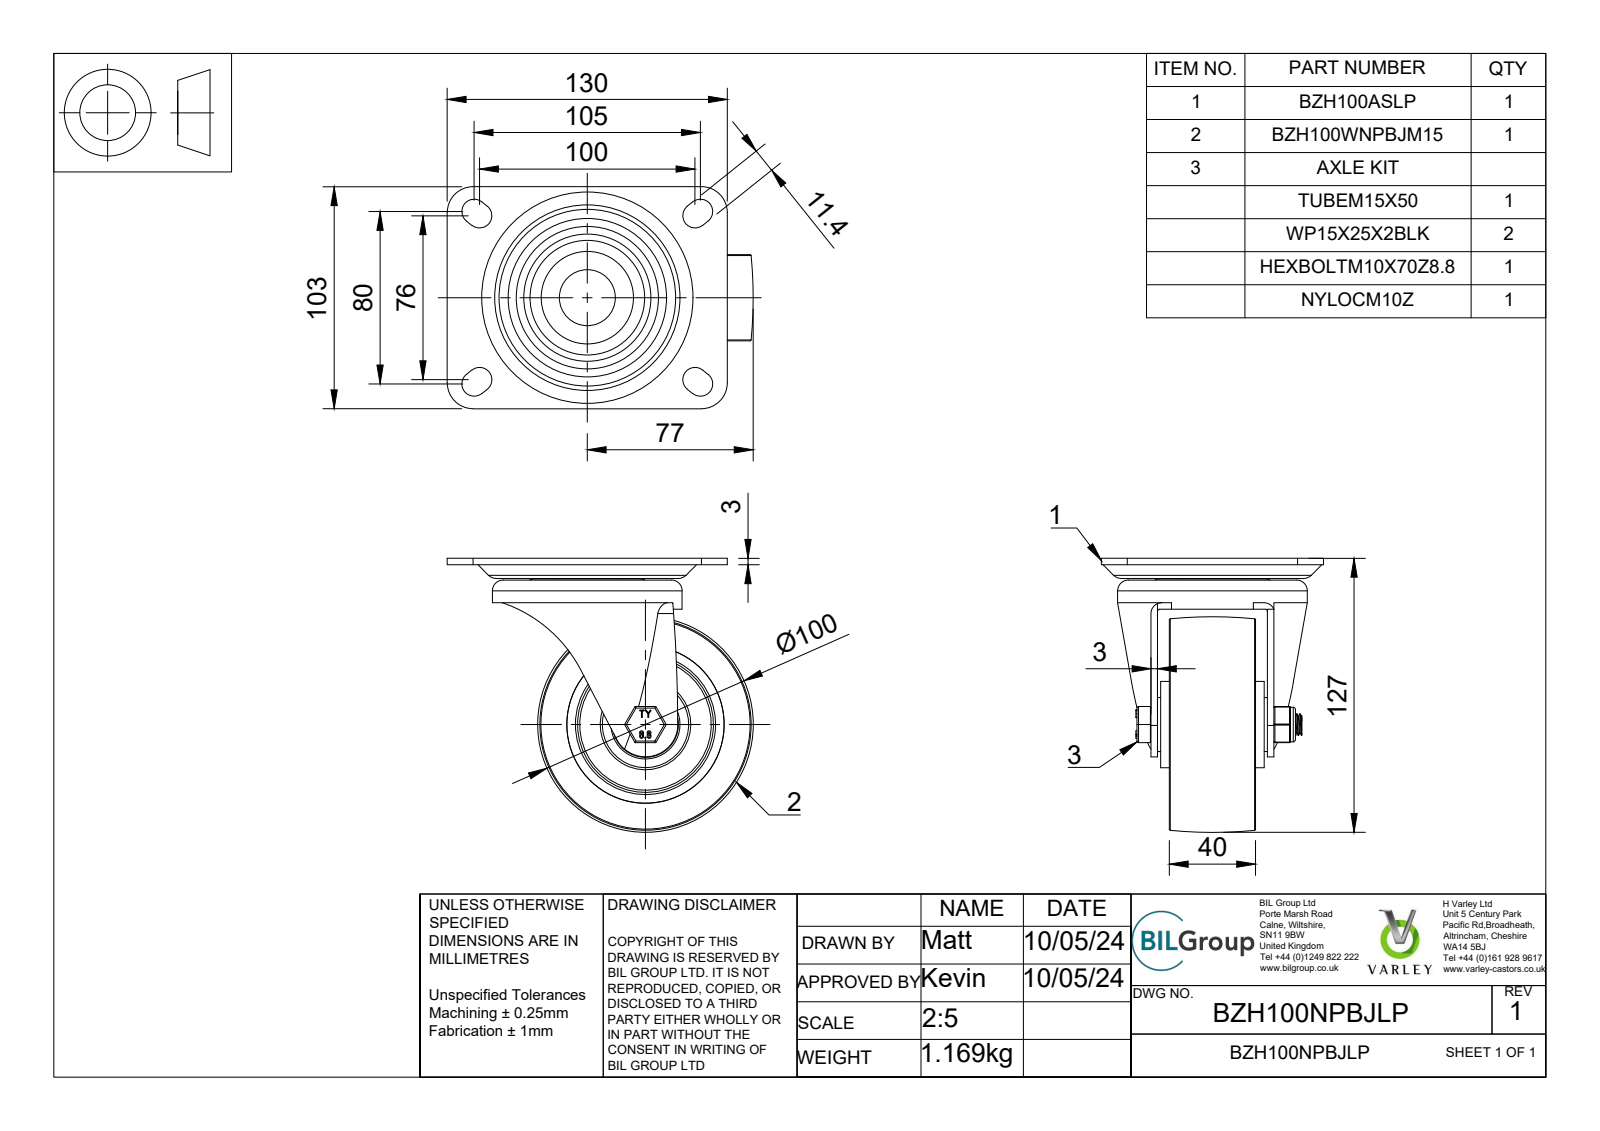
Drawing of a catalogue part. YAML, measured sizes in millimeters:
part_name: "BZH100NPBJLP v3; BZH100ASLP v1; ZINC PLATED PRESSED STEEL FORK; ZINC PLATED PRESSED STEEL TOP PLATE (+7 more)"
step_written_by: "Autodesk Translation Framework v12.20.1.177 (AUTOMOTIVE_DESIGN)"
units: millimeters
bodies: {solids: 39, faces: 1078, planar: 367, cylindrical: 187, other: 524}
overall_size: [142, 127.13, 103]
volume: 339463
surface_area: 150239
round_holes:
  - {diameter: 10, count: 1}
  - {diameter: 10.5, count: 1}
  - {diameter: 12, count: 1}
  - {diameter: 15, count: 1}
  - {diameter: 15.75, count: 1}
  - {diameter: 20.5, count: 1}
  - {diameter: 26.8, count: 1}
  - {diameter: 28, count: 1}
  - {diameter: 28.2, count: 1}
  - {diameter: 30, count: 1}
  - {diameter: 32, count: 1}
  - {diameter: 63, count: 1}
round_bosses_or_shafts:
  - {diameter: 88, count: 1}
  - {diameter: 40, count: 1}
  - {diameter: 36, count: 1}
  - {diameter: 30, count: 1}
  - {diameter: 28, count: 1}
  - {diameter: 26, count: 1}
  - {diameter: 25, count: 1}
  - {diameter: 21.5, count: 1}
partial_cylinders:
  - {radius: 0.5, count: 18}
  - {radius: 5.7, count: 8}
  - {radius: 0.75, count: 6}
  - {radius: 12, count: 4}
  - {radius: 1, count: 2}
  - {radius: 5, count: 2}
  - {radius: 11.4, count: 1}
  - {radius: 12.9, count: 1}
face_to_face_distances: [3, 40, 17.5, 22.5, 4, 26, 23, 54, 4.5, 5]
